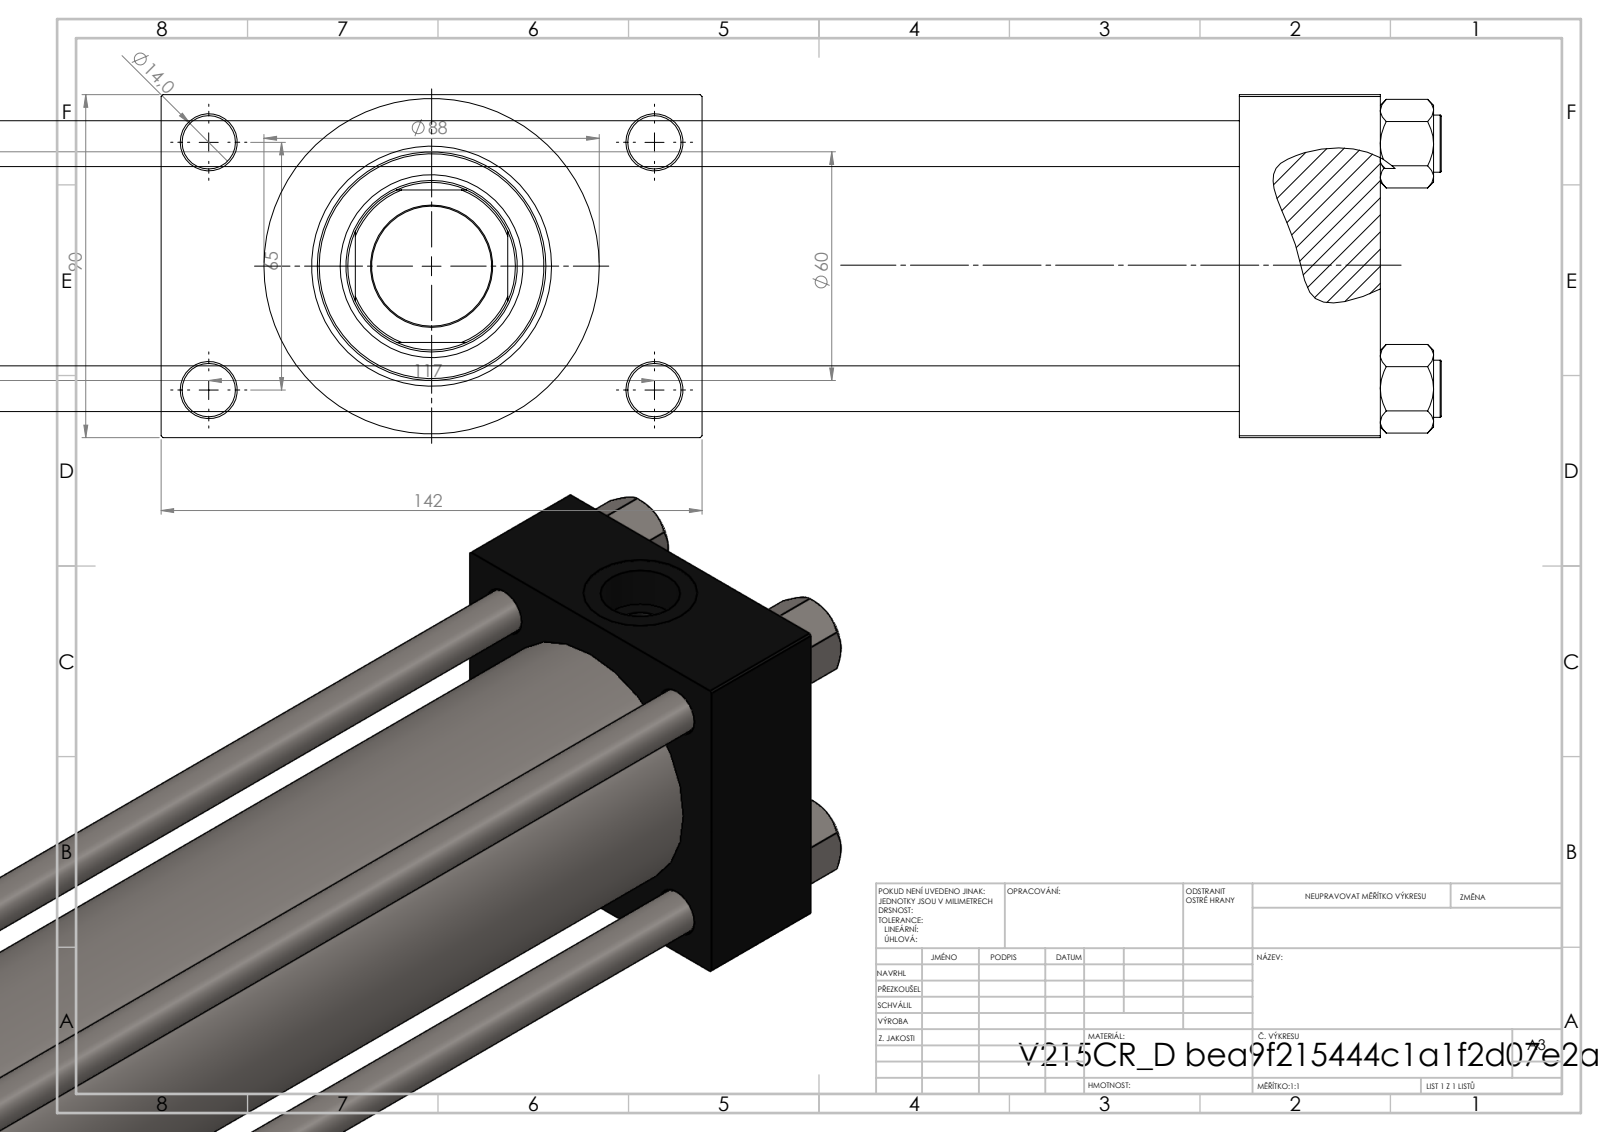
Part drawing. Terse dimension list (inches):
name: V215CR_D_TYCINKA; NUT_M5_D; V215_VC_A; V215CR_D_Body (+1 more)
written by: SolidWorks 2019 (CONFIG_CONTROL_DESIGN)
unit: in
bodies: 10 solids, 1103 faces (496 planar, 87 cylindrical, 520 other)
size: 20.984 × 5.591 × 3.543
volume: 64.93 in³; area: 688.1 in²
holes: 4× ⌀0.472, 4× ⌀0.551, 2× ⌀0.276, 2× ⌀0.825, 2× ⌀1.181, 1× ⌀1.24, 1× ⌀1.772, 1× ⌀1.89, 1× ⌀1.969, 1× ⌀2.362, 1× ⌀2.48
bosses: 4× ⌀0.591, 1× ⌀3.465, 1× ⌀2.717
rounds: 1× R0.866
face distances: 3.543, 15.315, 1.457, 16.772, 1.024, 4.567, 18.504, 17.047, 1.732, 5.591
hole spacings: 1.037, 1.79, 2.531, 2.635, 2.748, 3.569, 4.383, 2.559
